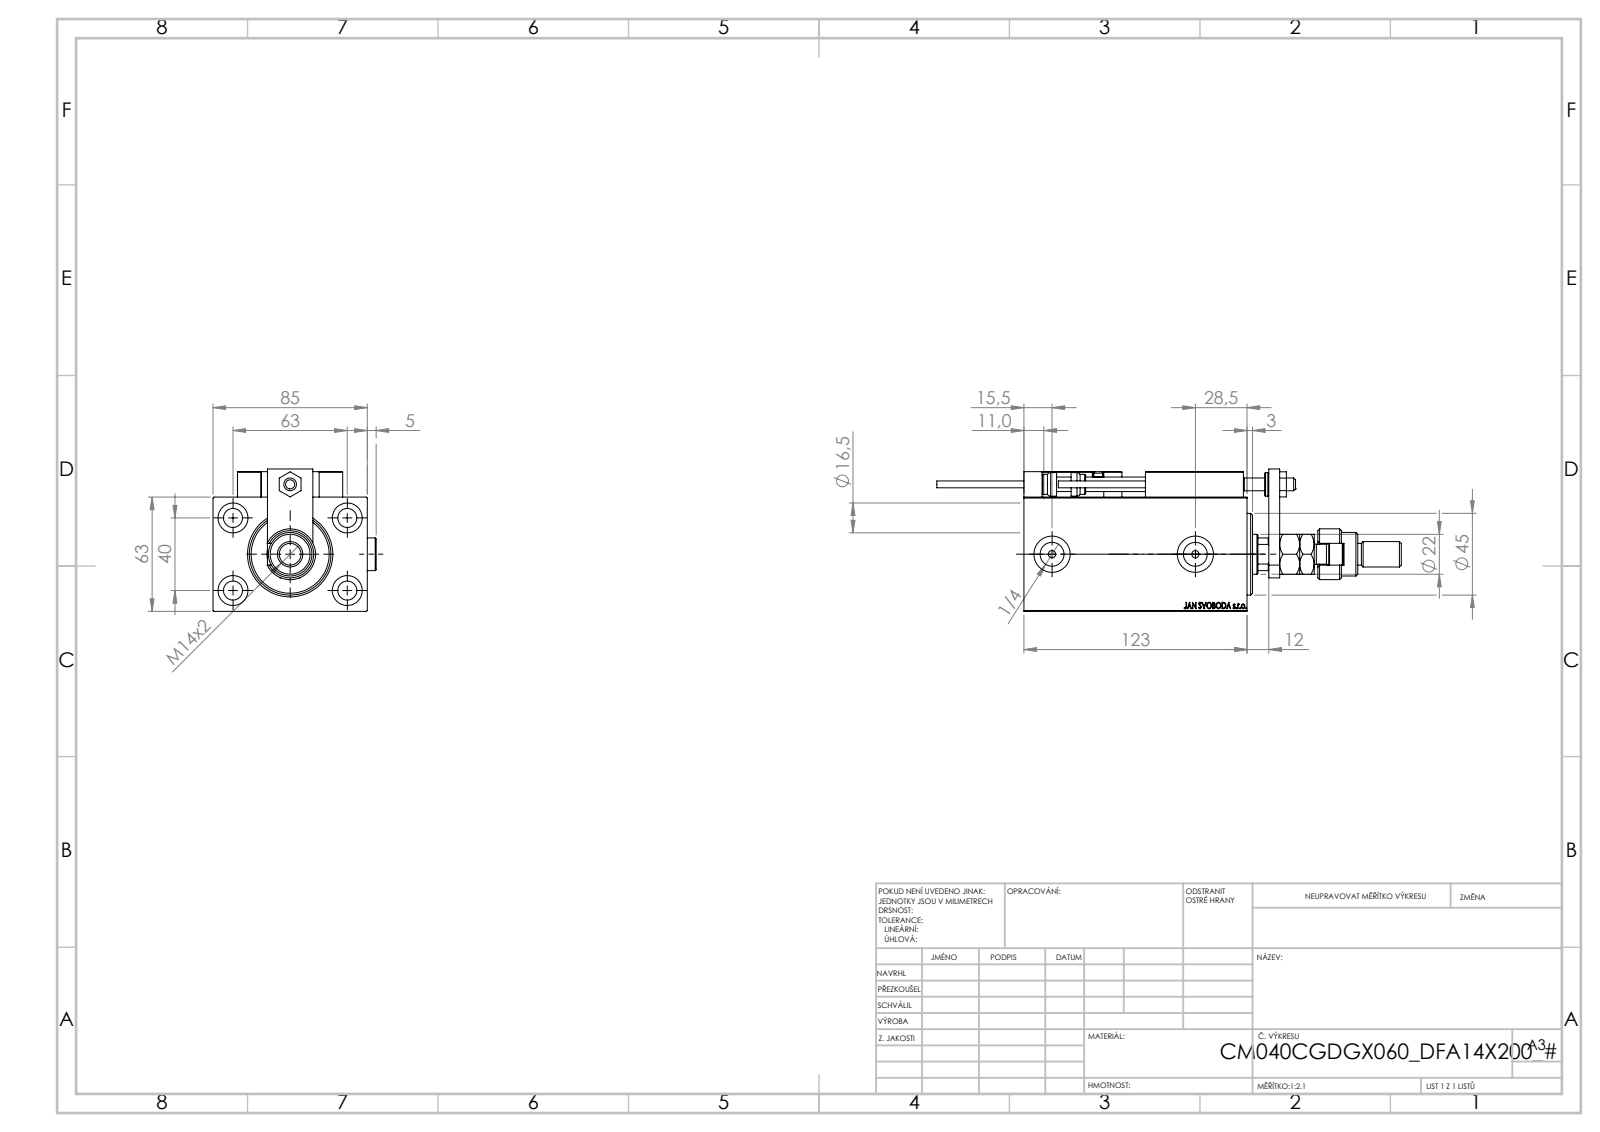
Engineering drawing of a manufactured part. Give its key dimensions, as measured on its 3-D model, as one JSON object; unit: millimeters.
{"part_name": "NUT_D12; ALLEN BOLT D8; V450CM_C_VCP; SWITCH X (+8 more)", "step_written_by": "SolidWorks 2019 (CONFIG_CONTROL_DESIGN)", "units": "millimeters", "bodies": {"solids": 27, "faces": 1421, "planar": 622, "cylindrical": 217, "other": 582}, "overall_size": [256, 89.9, 78.5], "volume_mm3": 624116, "surface_area_mm2": 135391, "round_holes": [[4, 6], [8, 5], [16.5, 5], [3.2, 4], [10.5, 4], [5, 2], [13.16, 2], [20, 2], [7, 1], [12.5, 1], [22, 1], [25.5, 1]], "round_bosses_or_shafts": [[18, 3], [11, 2], [5, 2], [3.8, 2], [28, 1], [24, 1], [14, 1], [13, 1]], "partial_cylinders_radius": [[0.3, 30], [3, 2], [9.75, 1], [10.5, 1]], "face_to_face_distances": [63, 85, 12, 111, 123, 14, 30, 18, 77, 6], "hole_center_spacings": [37.31, 11.37, 20, 29.59, 29.69, 36.06, 36.53, 40]}
